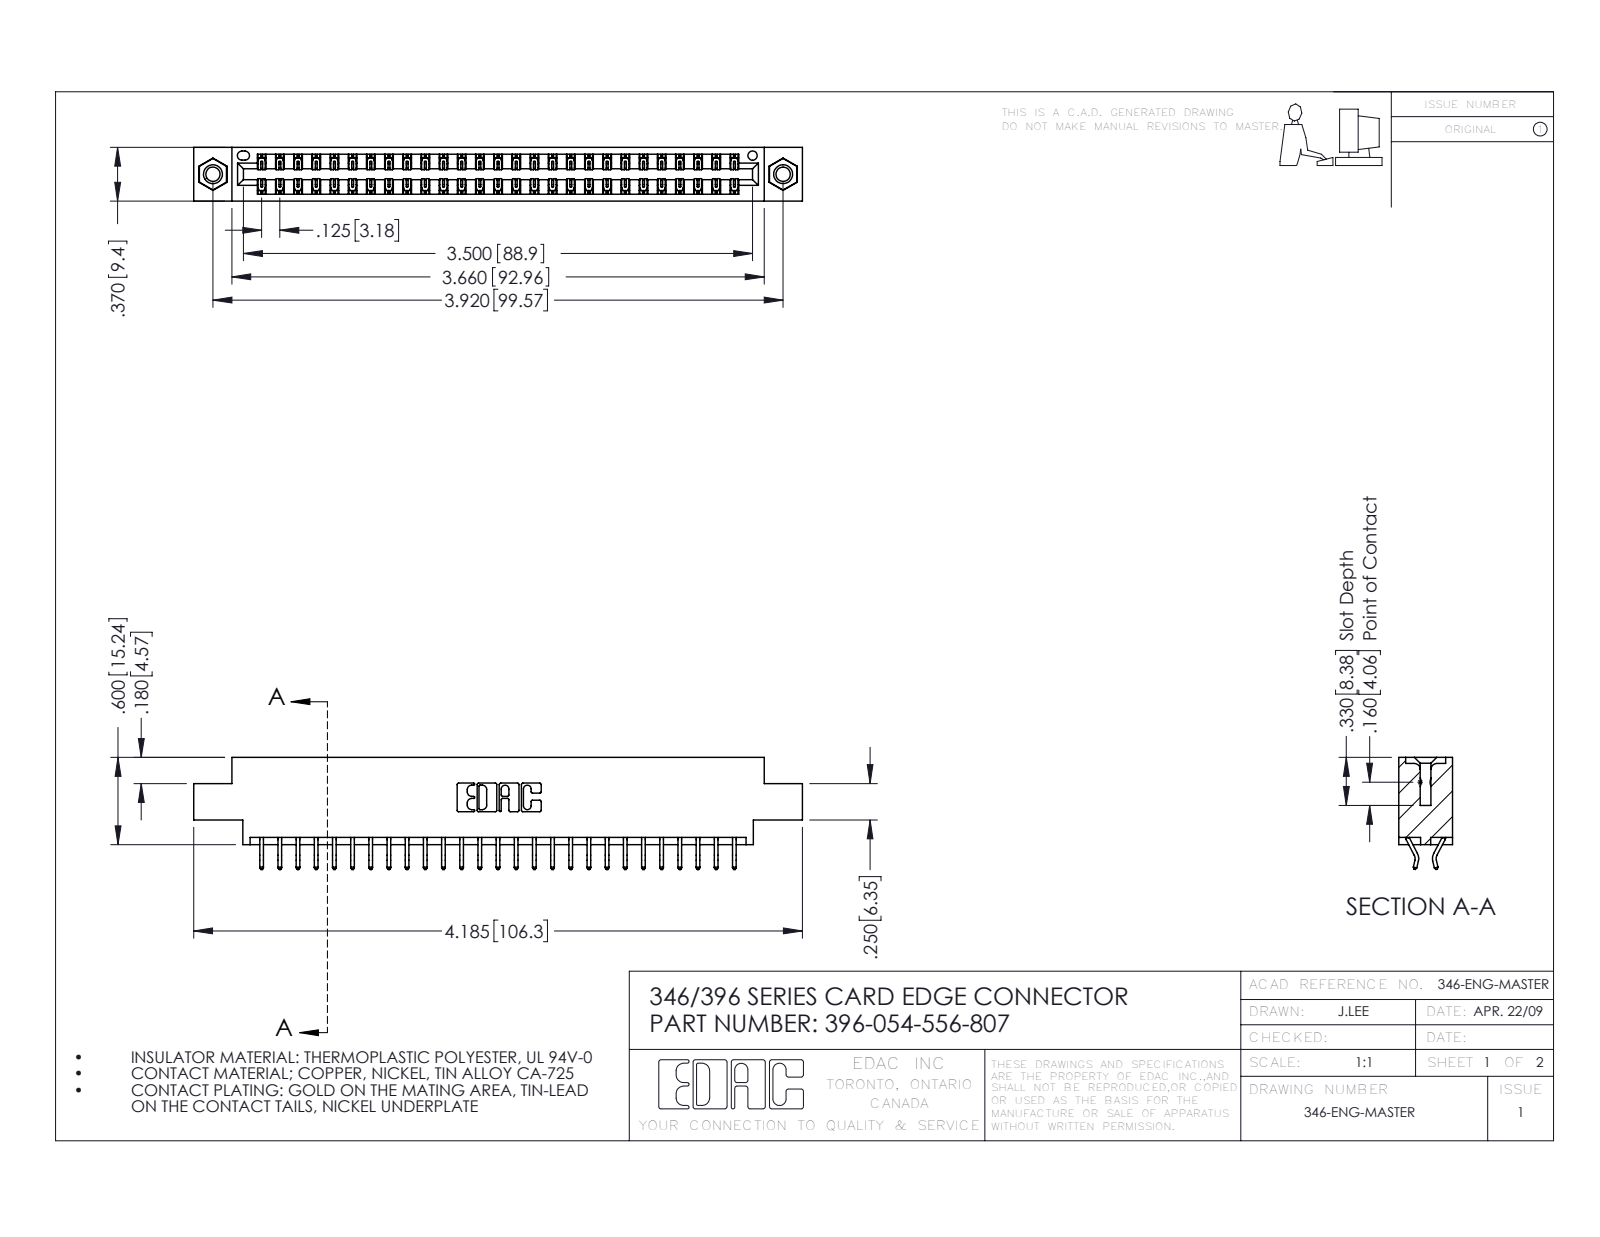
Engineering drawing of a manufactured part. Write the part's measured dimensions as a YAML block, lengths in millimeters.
part_name: "396-054-556-807; 345-250-001_345-250-005-103; 345-292-001_556 Tail; 346 Part_0.170 Offset - 0.156 Dia-TI"
step_written_by: "SolidWorks 2016 (CONFIG_CONTROL_DESIGN)"
units: millimeters
bodies: {solids: 57, faces: 3318, planar: 2218, cylindrical: 1084, other: 16}
overall_size: [106.3, 19.6, 9.4]
volume: 10100
surface_area: 13780
round_holes:
  - {diameter: 2.5, count: 2}
  - {diameter: 3.2, count: 2}
  - {diameter: 4, count: 2}
  - {diameter: 1.6, count: 1}
round_bosses_or_shafts:
  - {diameter: 3.9, count: 2}
partial_cylinders:
  - {radius: 0.2, count: 81}
  - {radius: 0.3, count: 22}
  - {radius: 0.2, count: 6}
  - {radius: 0.8, count: 6}
  - {radius: 0.7, count: 3}
  - {radius: 0.3, count: 2}
  - {radius: 0.4, count: 2}
  - {radius: 0.6, count: 2}
face_to_face_distances: [1.2, 8.2, 9.4, 6.4, 0.6, 1.8, 7.6, 7, 5.6, 3.8]
hole_center_spacings: [6.2, 94.3, 99.6]
